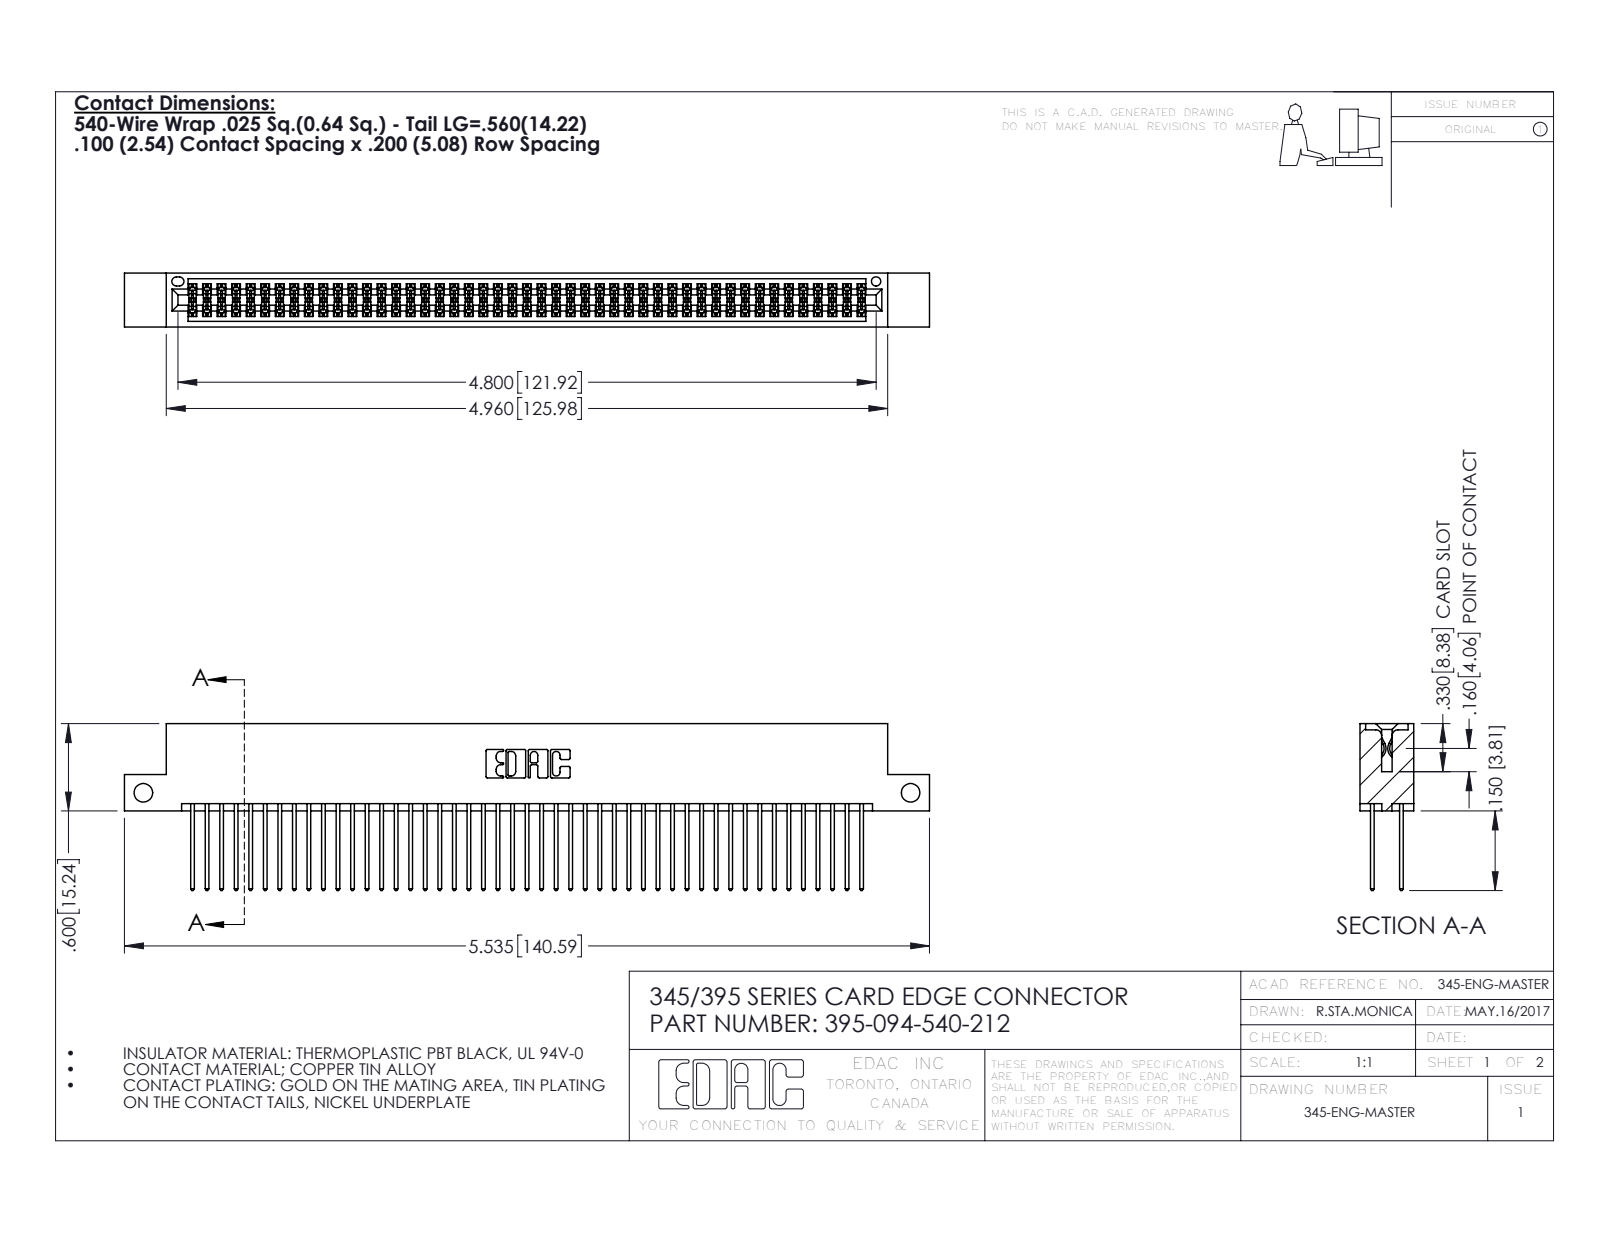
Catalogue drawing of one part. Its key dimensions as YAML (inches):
part_name: "345-292-001_345-293-140; 395-094-540-212; 345 Part_Flush Mounting Lugs - Side Mount"
step_written_by: "SolidWorks 2016 (CONFIG_CONTROL_DESIGN)"
units: inches
bodies: {solids: 95, faces: 4826, planar: 3182, cylindrical: 1644, other: 0}
overall_size: [5.535, 1.147, 0.37]
volume: 0.853
surface_area: 34.52
round_holes:
  - {diameter: 0.128, count: 2}
  - {diameter: 0.064, count: 1}
partial_cylinders:
  - {radius: 0.006, count: 141}
  - {radius: 0.01, count: 94}
  - {radius: 0.01, count: 22}
  - {radius: 0.007, count: 6}
  - {radius: 0.031, count: 6}
  - {radius: 0.026, count: 3}
  - {radius: 0.014, count: 2}
  - {radius: 0.019, count: 2}
face_to_face_distances: [0.298, 0.072, 0.2, 0.098, 0.272, 0.025, 0.37, 0.225, 0.175, 0.149]
hole_center_spacings: [5.275]
